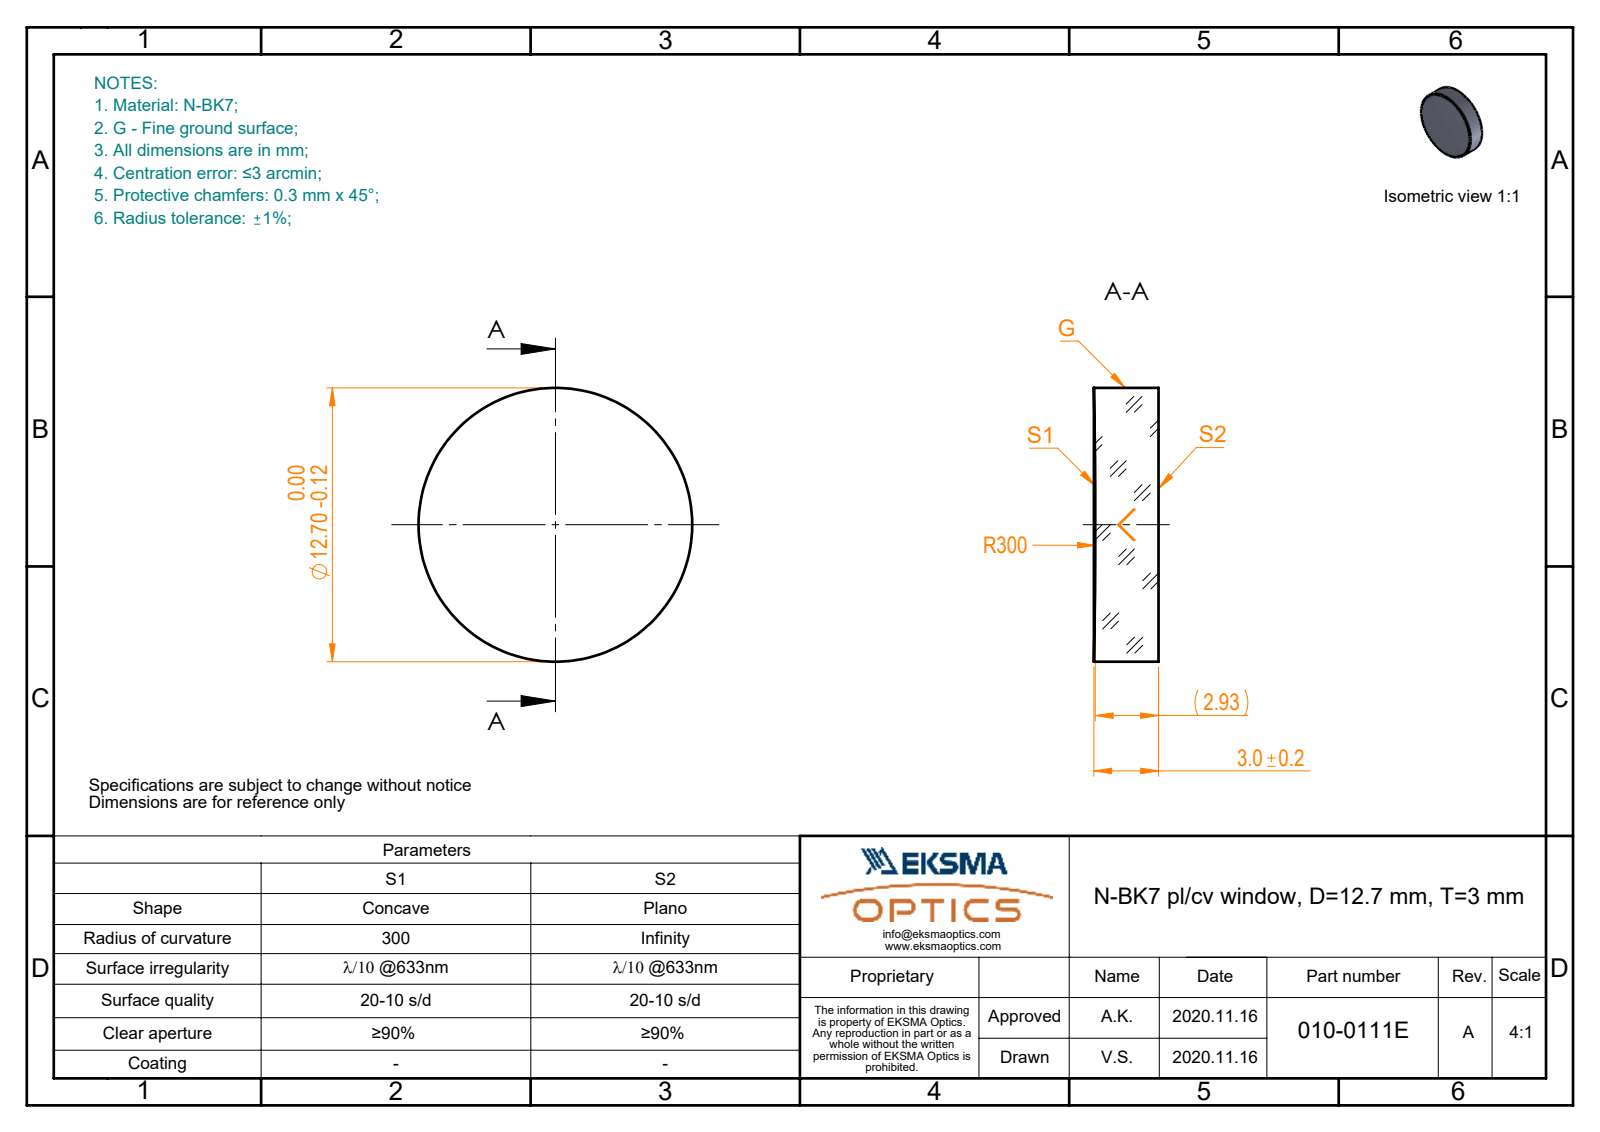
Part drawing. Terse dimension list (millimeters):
name: 010-0111E_N-BK7_PCV_window
written by: SolidWorks 2019 (CONFIG_CONTROL_DESIGN)
unit: mm
bodies: 1 solid, 5 faces (1 planar, 2 cylindrical, 2 other)
size: 12.7 × 12.7 × 3
volume: 376 mm³; area: 373 mm²
bosses: 1× ⌀12.7
